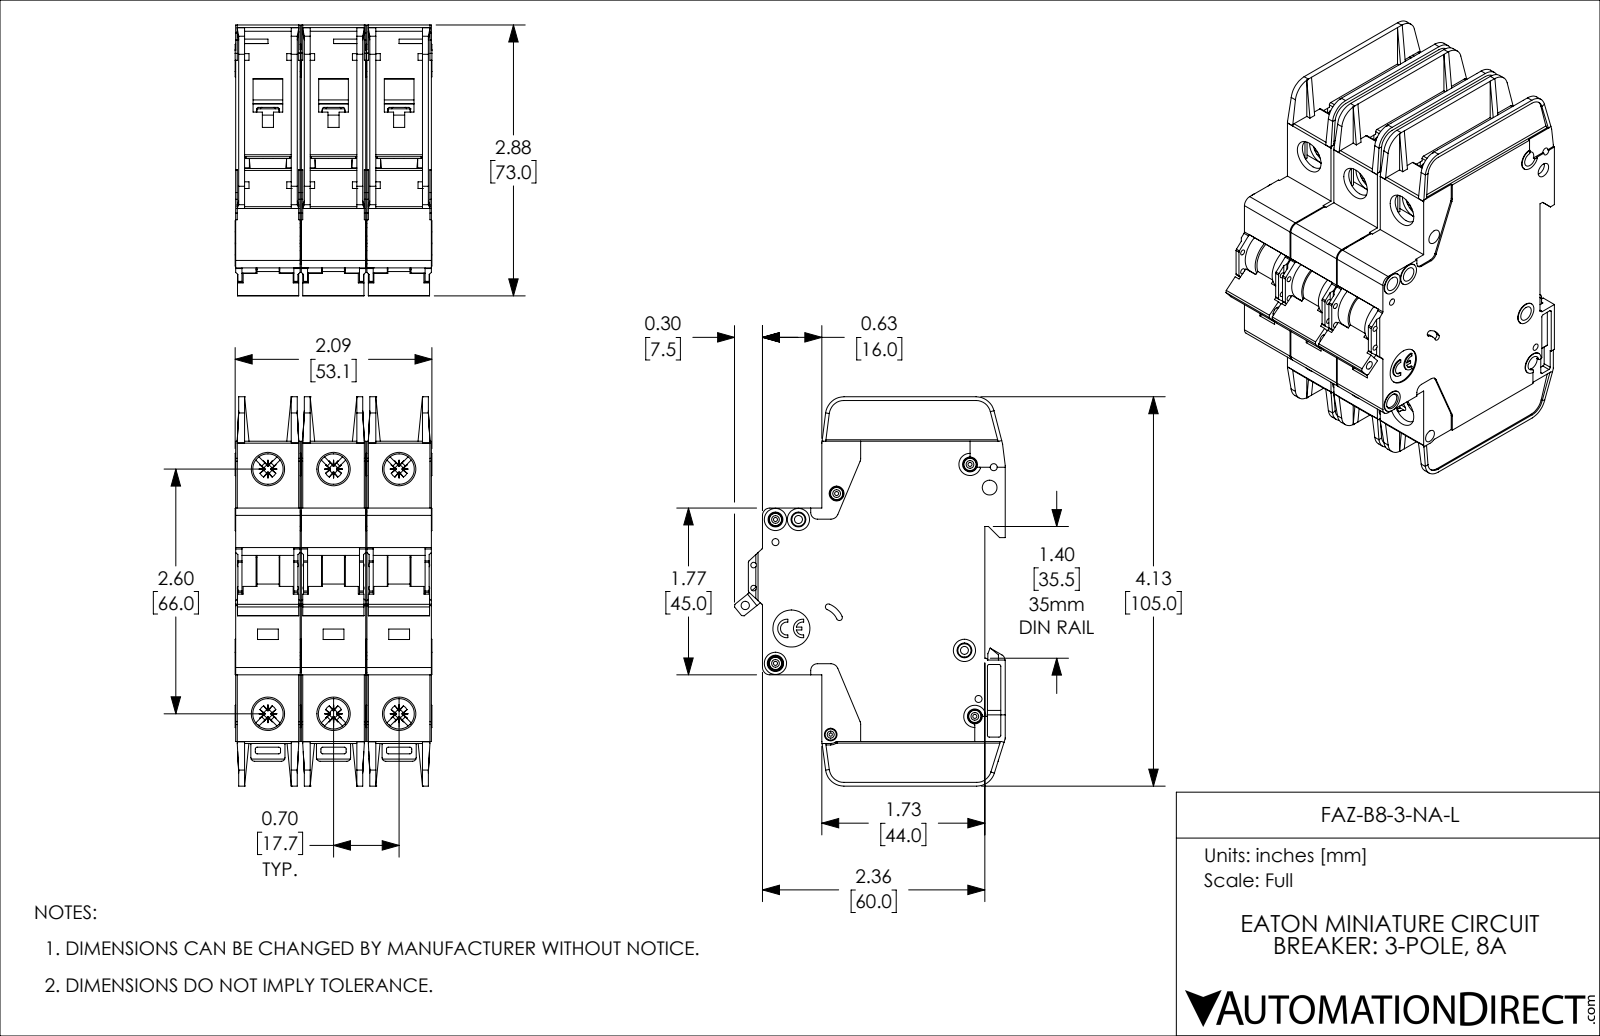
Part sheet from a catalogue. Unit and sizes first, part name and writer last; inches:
Units: inches
Overall size (bounding box): 4.134 × 2.876 × 2.091
Round holes (diameter × count): ⌀0.157 ×8, ⌀0.323 ×6, ⌀0.043 ×5, ⌀0.075 ×4, ⌀0.059 ×2, ⌀0.085 ×2, ⌀0.035 ×1, ⌀0.089 ×1, ⌀0.098 ×1, ⌀0.134 ×1, ⌀0.394 ×1
Round bosses / shafts (diameter × count): ⌀0.13 ×5, ⌀0.236 ×4, ⌀0.118 ×4, ⌀0.098 ×3
Partial cylindrical surfaces — rounded edges, fillets, slot ends (radius × count): R0.02 ×72, R0.016 ×30, R0.039 ×18, R0.043 ×12, R0.079 ×12, R0.008 ×6, R0.01 ×6, R0.028 ×6
Main face-to-face distances: 0.697, 0.047, 1.394, 0.685, 0.591, 1.382, 0.744, 0.65, 0.106, 0.094
Hole centre spacings: 0.697, 2.69, 2.598, 0.244, 0.537, 0.87, 1.394, 2.948
Volume: 14.05 in³ · Surface area: 123 in²
Bodies: 3 solids, 3381 faces (2013 planar, 1071 cylindrical, 297 other)
Part name (STEP PRODUCT): FAZ-B8-3-NA-L
STEP written by: SolidWorks 2019 (AUTOMOTIVE_DESIGN)
